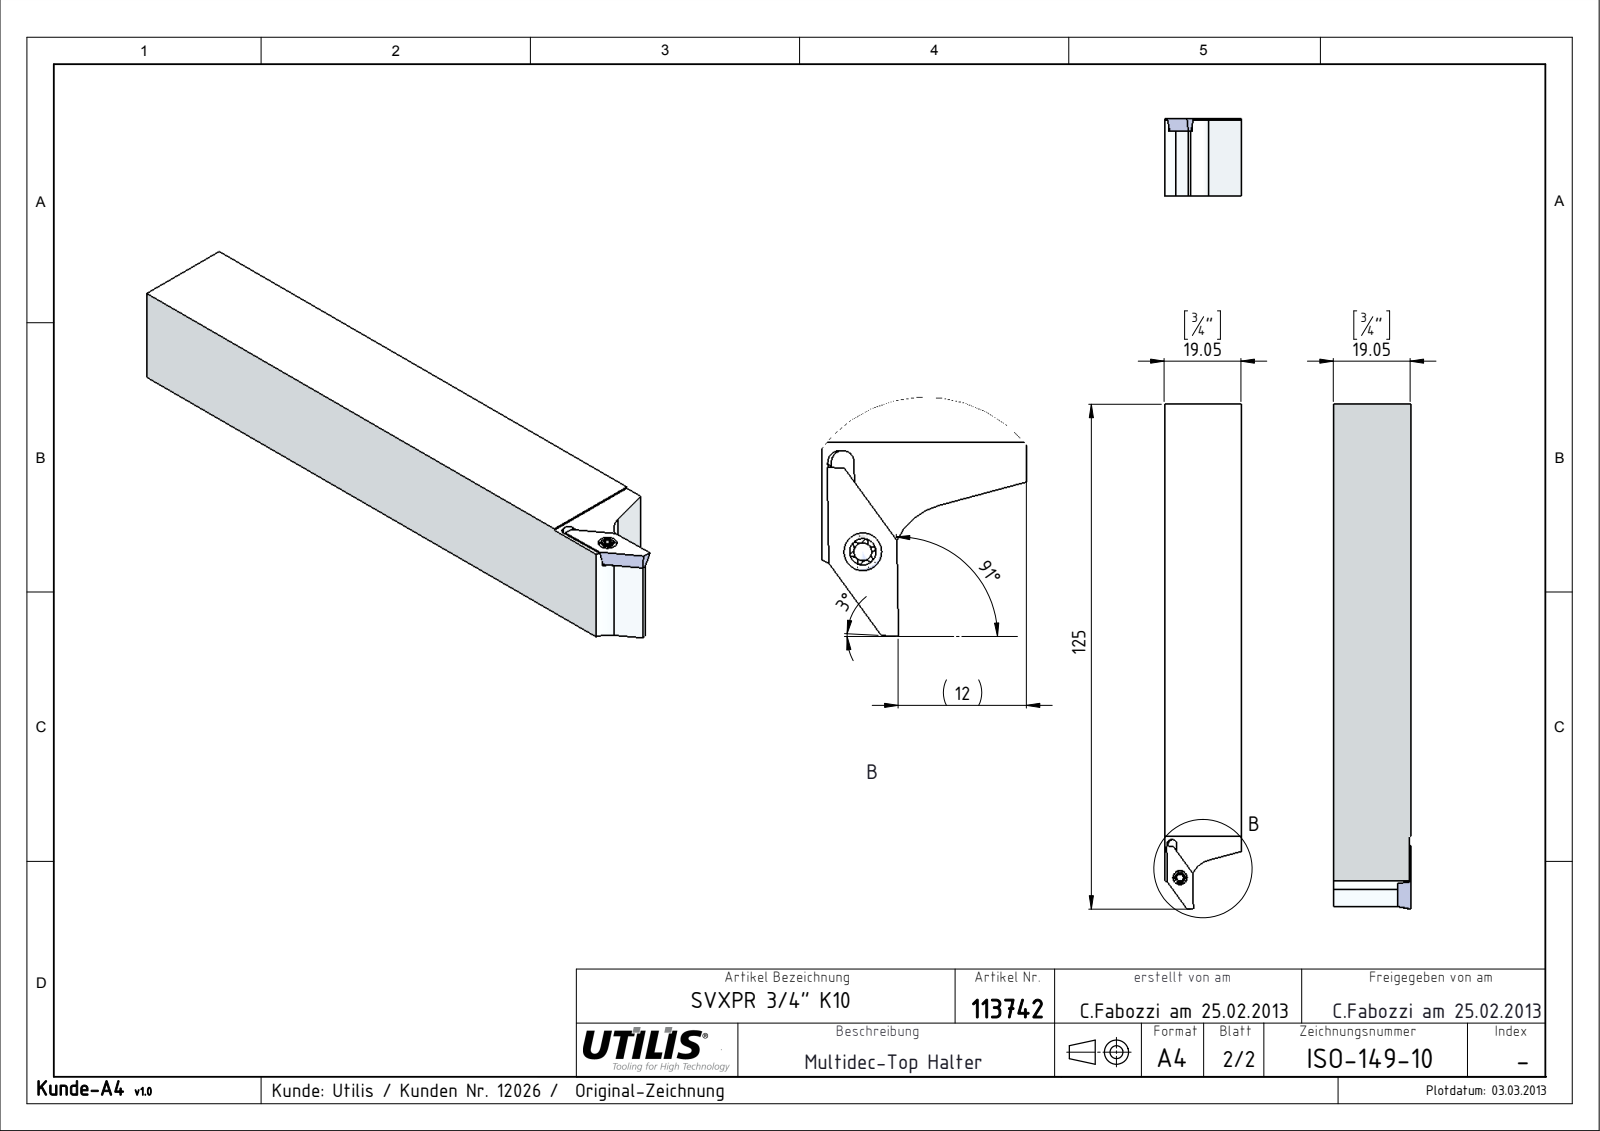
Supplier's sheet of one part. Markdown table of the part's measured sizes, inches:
| quantity | value |
| --- | --- |
| part name | MSP-7_M2,5X6-TX8 CERATIZIT Schraube; ISO-149-10; VPGT 10 R_VPGT 10 R; ISO-149-Kunde_10 |
| STEP written by | SolidWorks 2015 (CONFIG_CONTROL_DESIGN) |
| units | inches |
| bodies | 3 solids, 72 faces (28 planar, 27 cylindrical, 17 other) |
| overall size | 4.921 × 0.75 × 0.75 |
| volume | 2.552 in³ |
| surface area | 15.69 in² |
| round holes (diameter × count) | 0.081 × 1, 0.118 × 1 |
| round bosses / shafts (diameter × count) | 0.136 × 1, 0.098 × 1 |
| partial cylindrical surfaces (radius × count) | 0.008 × 6, 0.018 × 6, 0.236 × 2, 0.041 × 1 |
| main face-to-face distances | 0.75, 0.738, 0.625, 0.113, 0.125, 0.21, 0.083, 0.127, 0.209, 4.213 |
